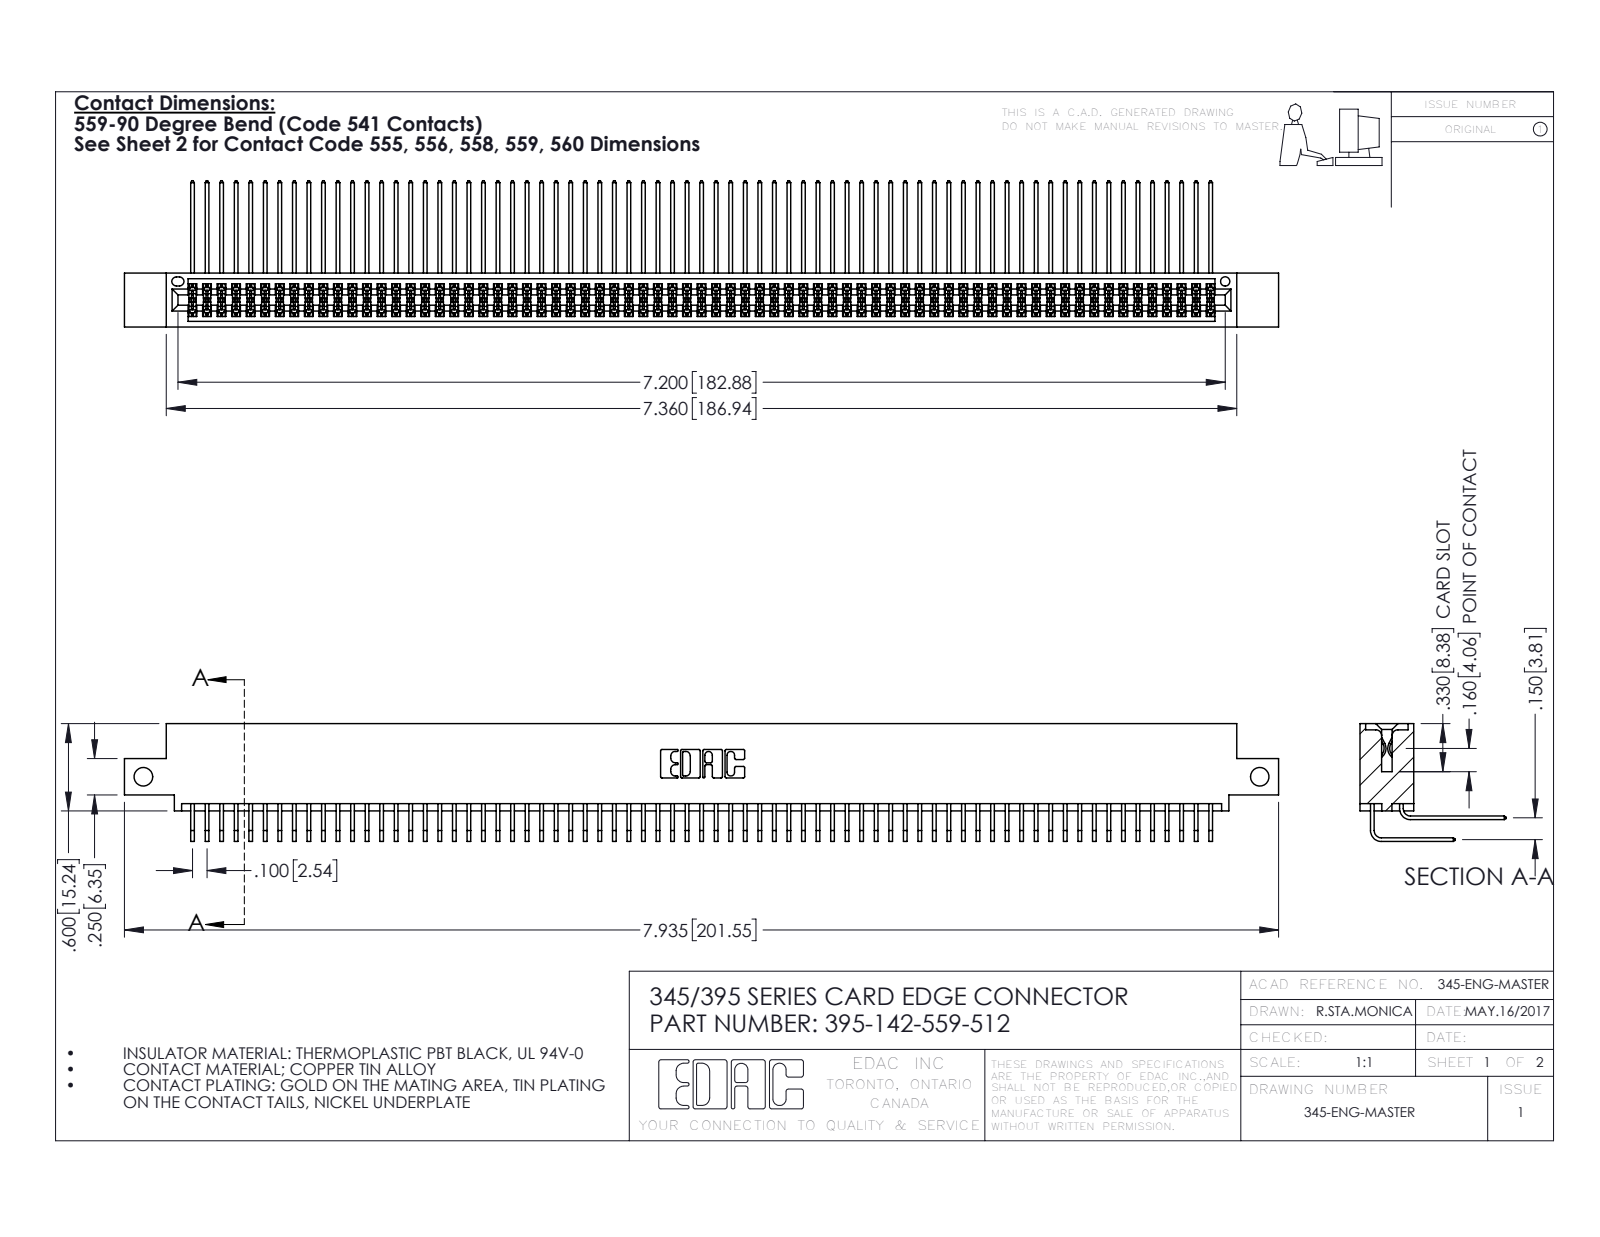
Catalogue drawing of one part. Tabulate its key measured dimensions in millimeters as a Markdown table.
| quantity | value |
| --- | --- |
| part name | 345 Part_0.110 Offset - Side Mount; 345-292-001_559 Tail - 2; 395-142-559-512; 345-292-001_558 559 Tail - 1 |
| STEP written by | SolidWorks 2016 (CONFIG_CONTROL_DESIGN) |
| units | millimeters |
| bodies | 143 solids, 7514 faces (5054 planar, 2460 cylindrical, 0 other) |
| overall size | 201.5 × 25.5 × 20.5 |
| volume | 20 500 mm³ |
| surface area | 34 680 mm² |
| round holes (diameter × count) | 3.3 × 2, 1.6 × 1 |
| partial cylindrical surfaces (radius × count) | 0.2 × 284, 0.3 × 22, 0.2 × 6, 0.8 × 6, 0.7 × 3, 0.4 × 2, 0.5 × 2, 0.6 × 2 |
| main face-to-face distances | 1.8, 7.6, 5.1, 9.4, 2.5, 6.9, 0.6, 5.7, 4.4, 3.8 |
| hole center spacings | 194.9 |
